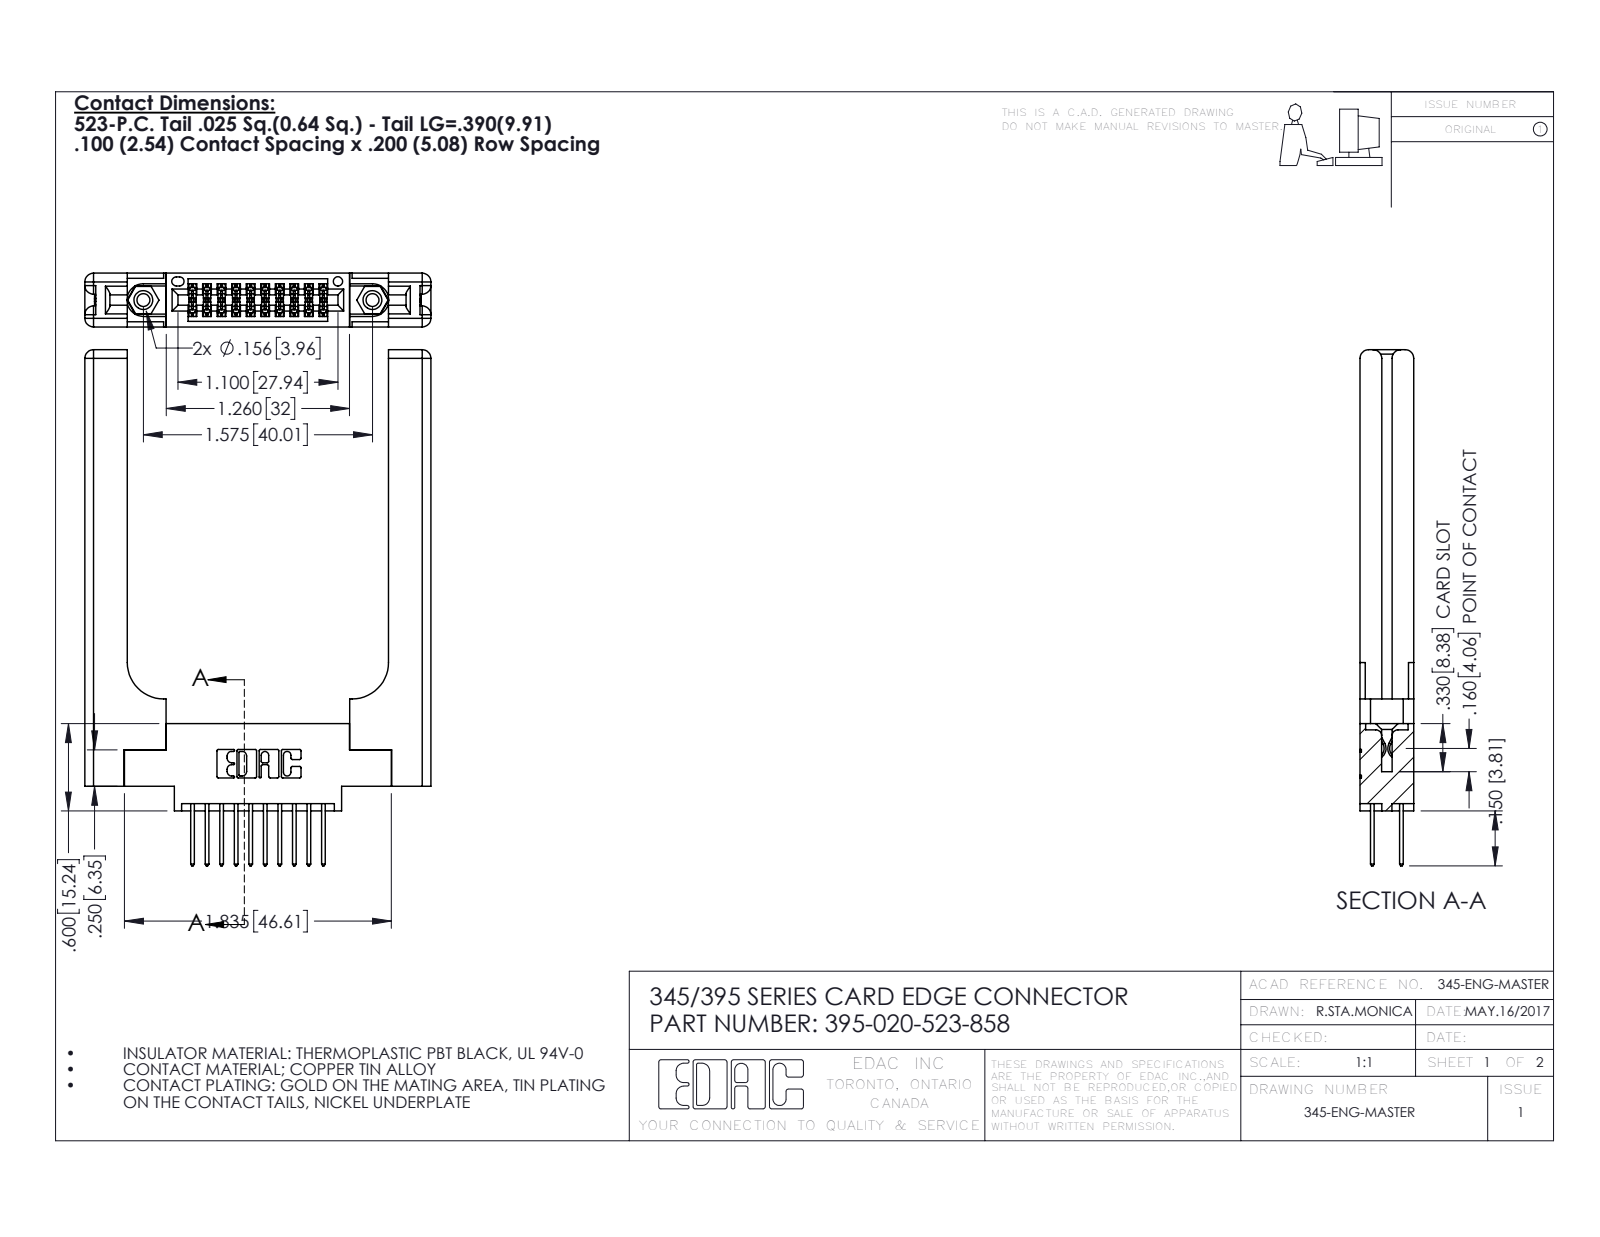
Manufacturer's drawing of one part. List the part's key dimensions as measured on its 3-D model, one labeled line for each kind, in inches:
Part name (STEP PRODUCT): 345 Part_0.170 Offset - 0.156 Dia-TH; 345-250-001_345-250-001-102; 345-220-058_345-220-058; 395-020-523-858 (+1 more)
STEP written by: SolidWorks 2016 (CONFIG_CONTROL_DESIGN)
Units: inches
Bodies: 25 solids, 1386 faces (892 planar, 434 cylindrical, 60 other)
Overall size (bounding box): 3.547 × 2.379 × 0.37
Volume: 0.853 in³ · Surface area: 19.99 in²
Round holes (diameter × count): ⌀0.089 ×2, ⌀0.125 ×2, ⌀0.156 ×2, ⌀0.064 ×1
Round bosses / shafts (diameter × count): ⌀0.155 ×2
Partial cylindrical surfaces — rounded edges, fillets, slot ends (radius × count): R0.006 ×30, R0.01 ×22, R0.01 ×20, R0.06 ×16, R0.007 ×6, R0.031 ×6, R0.026 ×3, R0.014 ×2
Main face-to-face distances: 0.37, 0.072, 0.298, 0.148, 0.15, 0.077, 0.22, 0.225, 0.123, 0.098
Hole centre spacings: 0.27, 1.344, 1.575
